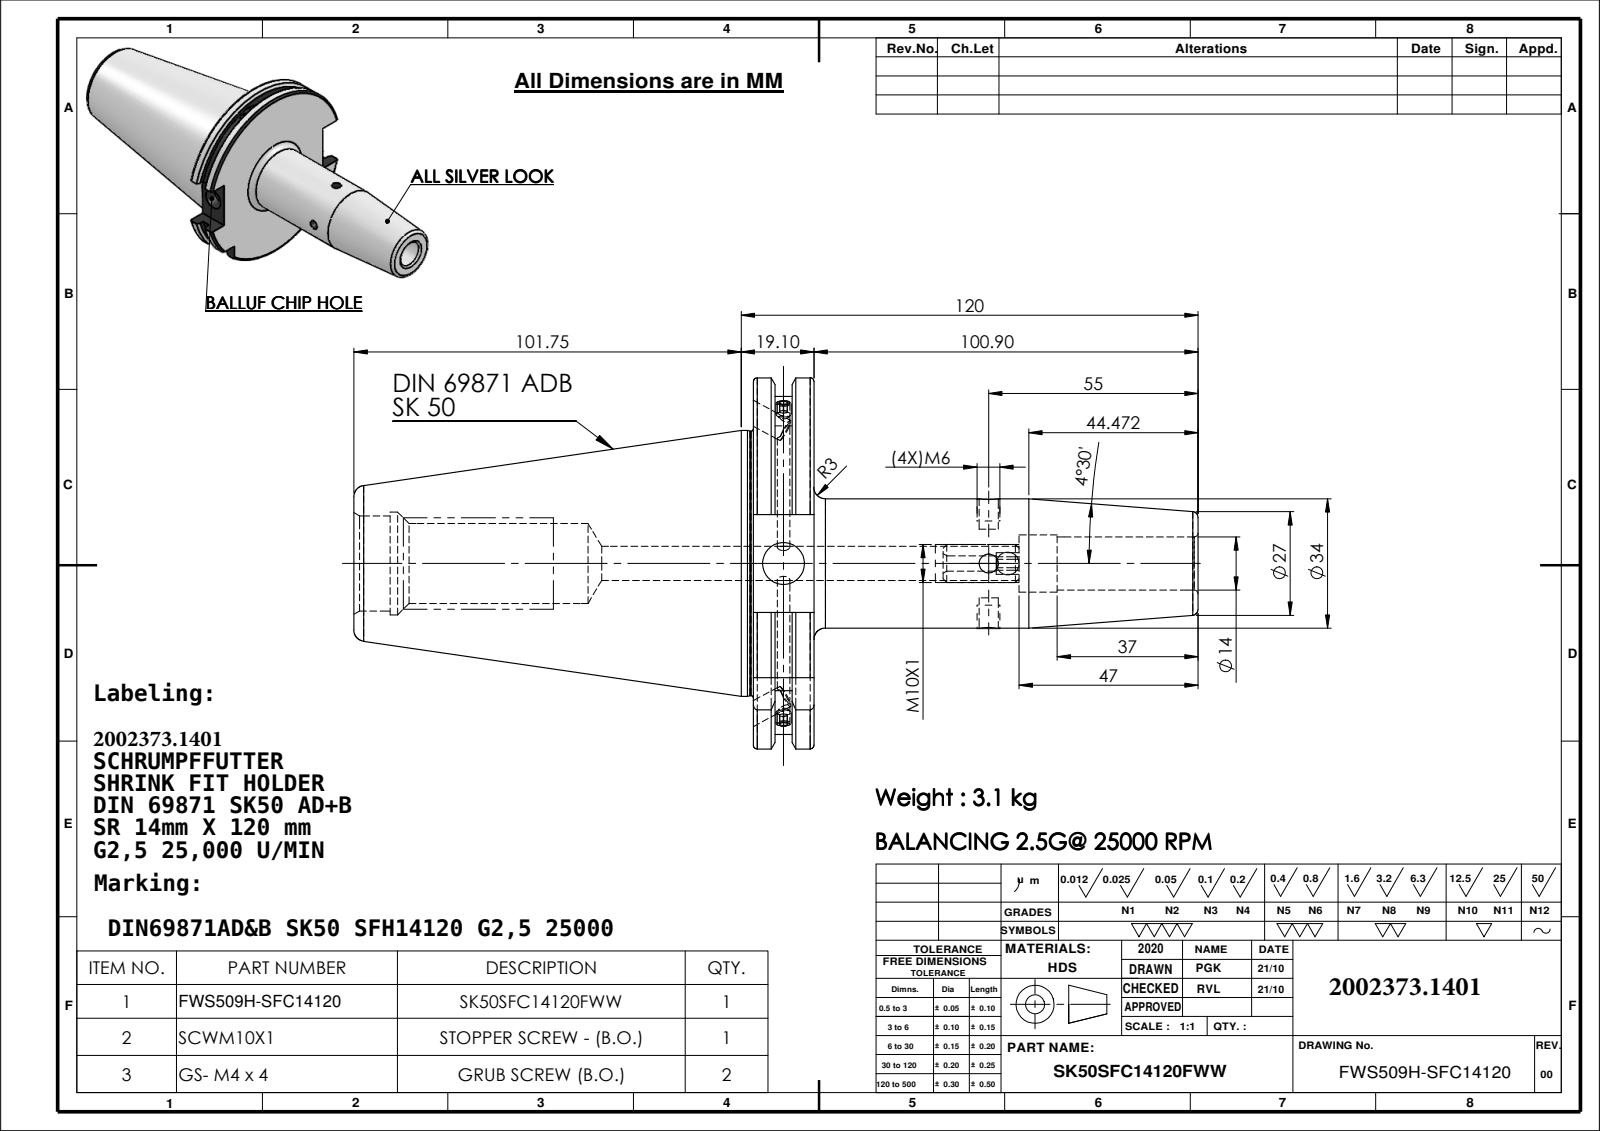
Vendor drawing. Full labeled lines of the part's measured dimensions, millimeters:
Part name (STEP PRODUCT): 91506-SR214120
STEP written by: SolidWorks 2018 (AUTOMOTIVE_DESIGN)
Units: millimetres
Bodies: 1 solid, 122 faces (29 planar, 53 cylindrical, 40 other)
Overall size (bounding box): 221.75 × 97.5 × 94.05
Volume: 406 472 mm³ · Surface area: 57 155 mm²
Round holes (diameter × count): ⌀5 ×2, ⌀6 ×2, ⌀3.3 ×1, ⌀9 ×1, ⌀11 ×1, ⌀13.99 ×1, ⌀15 ×1, ⌀21 ×1, ⌀25 ×1, ⌀27 ×1
Round bosses / shafts (diameter × count): ⌀69.85 ×1, ⌀69.45 ×1, ⌀34 ×1
Partial cylindrical surfaces — rounded edges, fillets, slot ends (radius × count): R44.9 ×1, R48.75 ×1
Main face-to-face distances: 15.9, 5.66, 10.24, 10.14, 4.48, 5.76, 104.95, 110.61, 115.09, 120.85
Hole centre spacings: 53.9
